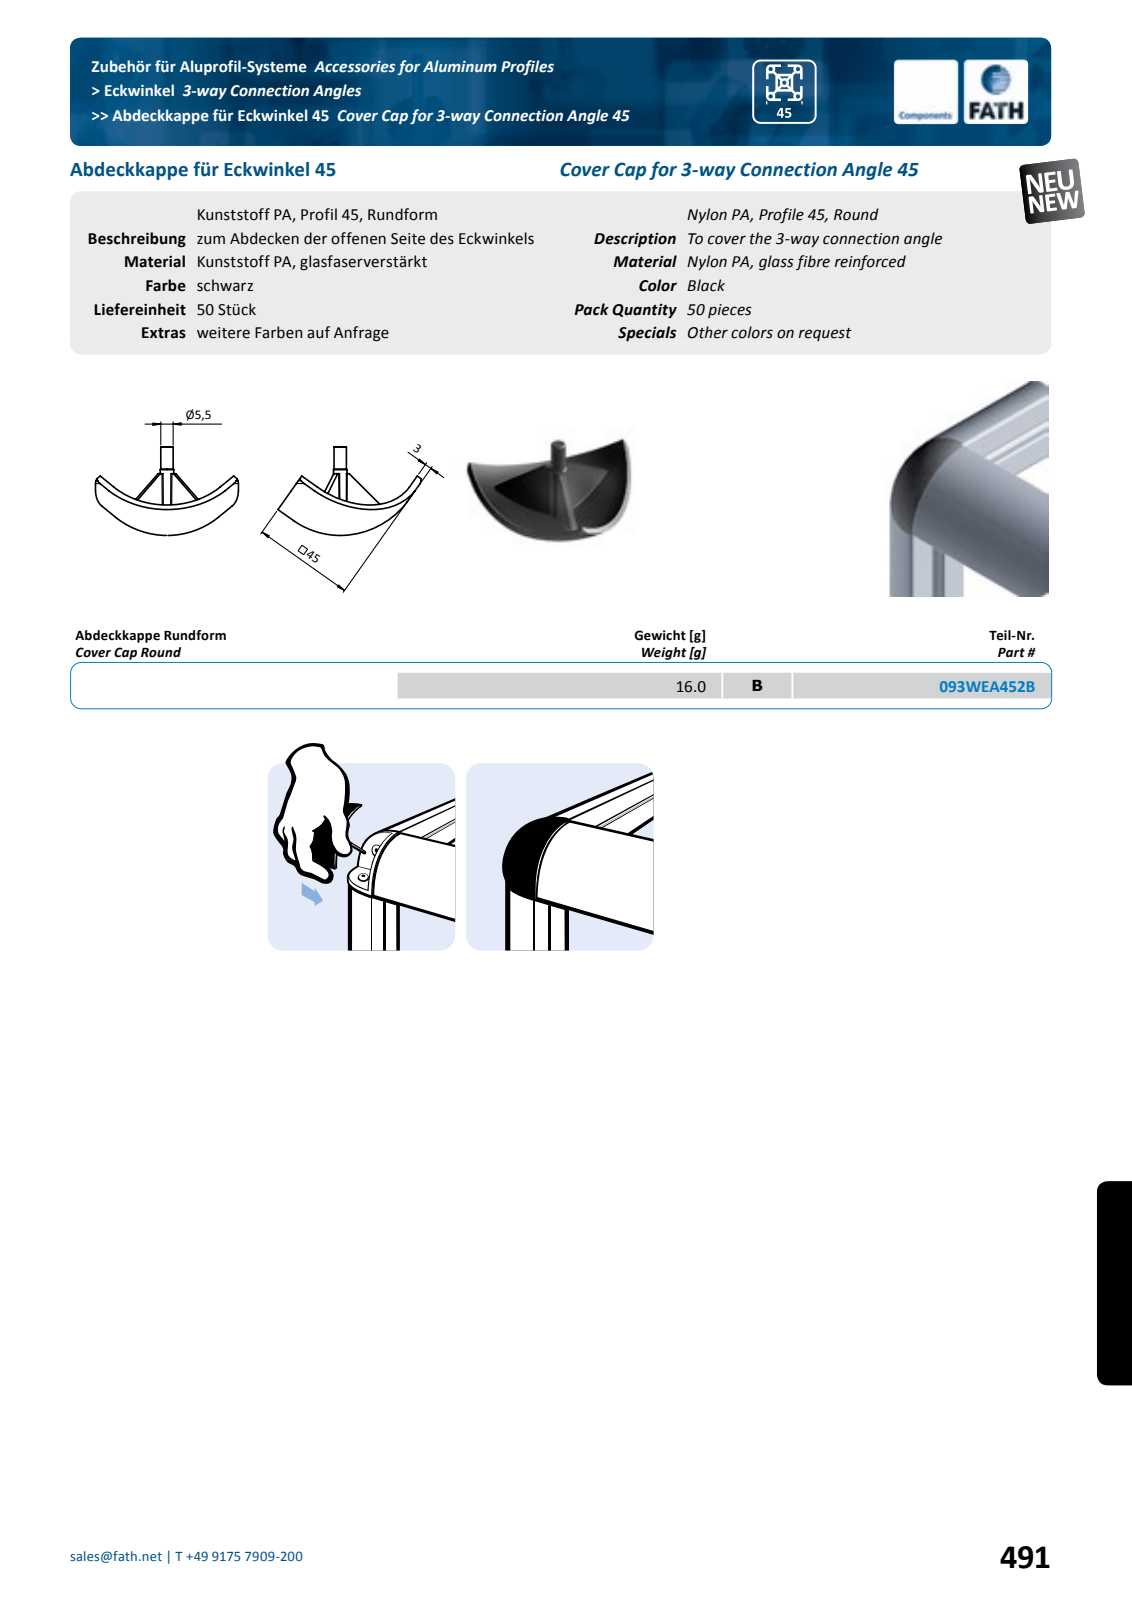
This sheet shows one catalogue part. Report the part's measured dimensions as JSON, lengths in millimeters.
{"part_name": "fath_093wea452b", "step_written_by": "Spatial InterOp 3D (automotive_design)", "units": "millimeters", "bodies": {"solids": 1, "faces": 70, "planar": 26, "cylindrical": 13, "other": 31}, "overall_size": [63.64, 48.02, 45], "volume_mm3": 12037, "surface_area_mm2": 9670, "round_bosses_or_shafts": [[6, 1], [5.5, 1]], "partial_cylinders_radius": [[2.5, 3], [33.5, 3], [37.78, 3]], "face_to_face_distances": [3, 41.99, 44.99, 42, 45, 11.99, 9.99, 2]}
